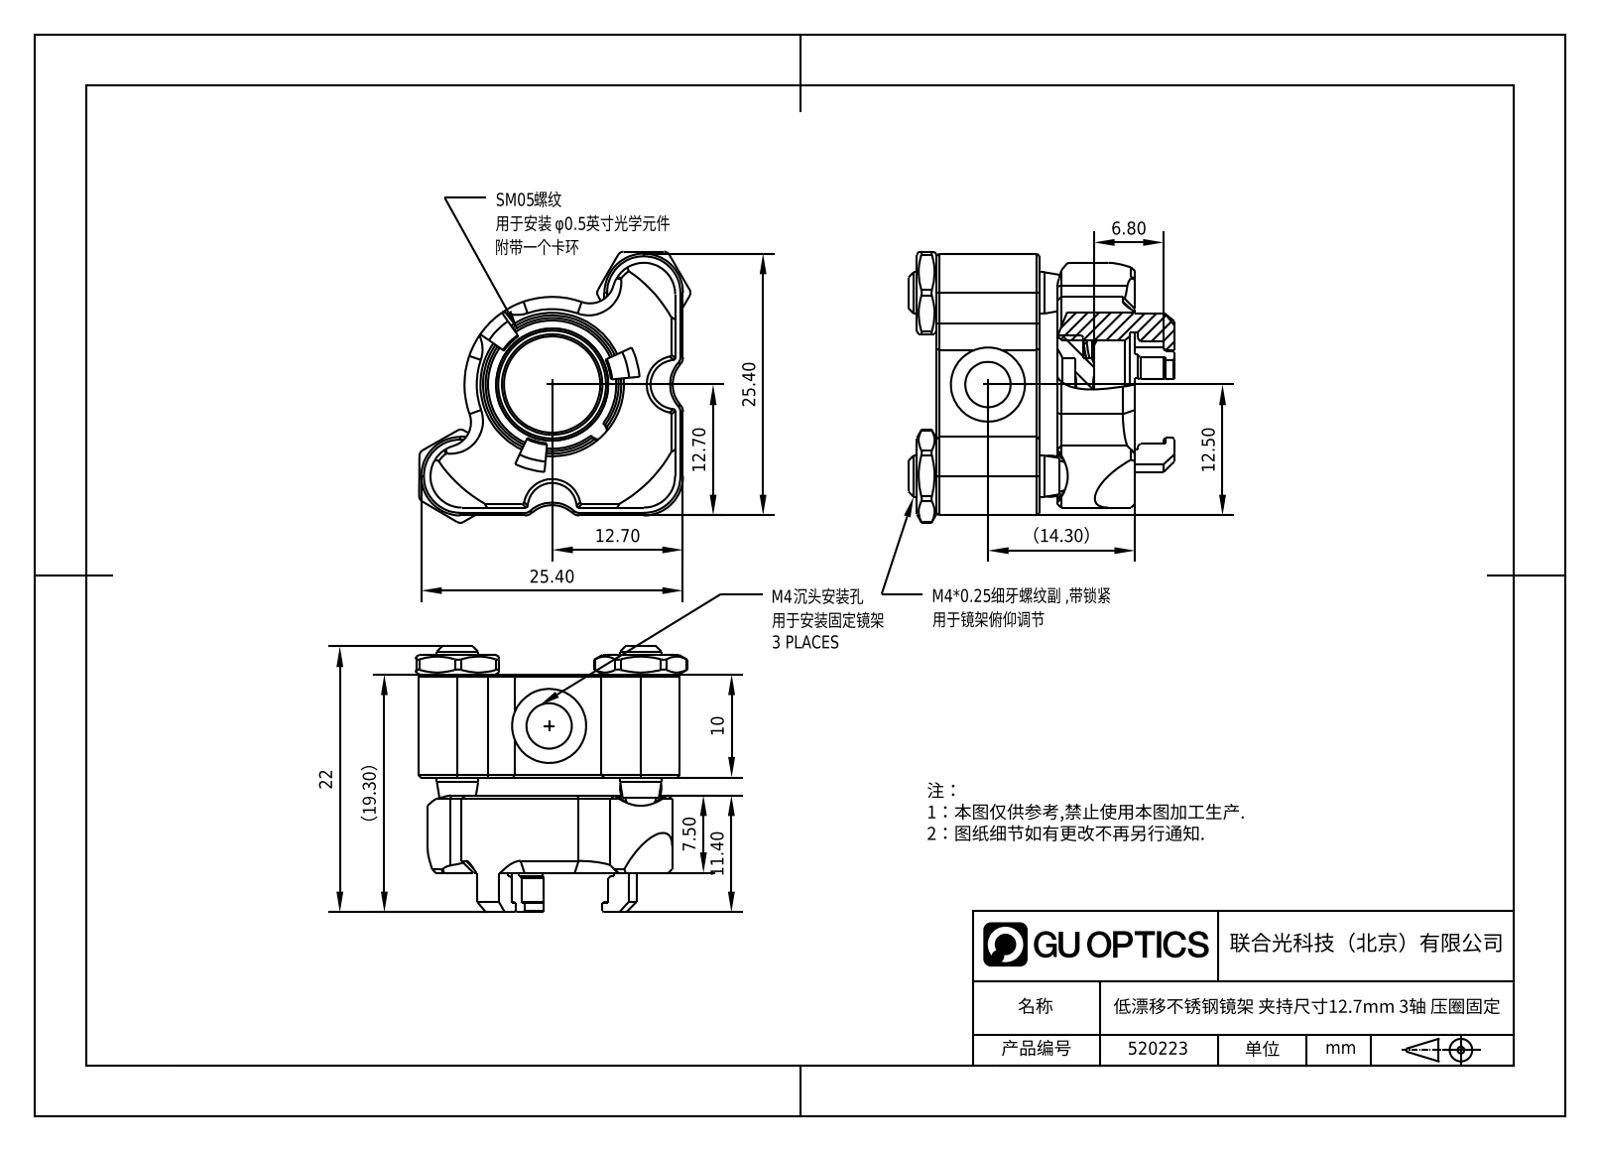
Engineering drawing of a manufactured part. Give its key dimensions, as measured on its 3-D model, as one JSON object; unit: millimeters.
{"part_name": "1.1.20.25_ZJO-PSM0.5-3; ZFK不锈钢透镜卡环压圈_1.8.9.1_ZFKS-K05; DXS-0425标准细牙螺丝_3.2.2.3-DXS-0425-16; 32.5.1-6，蓝宝石垫片，A (+5 more)", "step_written_by": "SolidWorks 2021 (CONFIG_CONTROL_DESIGN)", "units": "millimeters", "bodies": {"solids": 20, "faces": 583, "planar": 193, "cylindrical": 171, "other": 219}, "overall_size": [26.33, 26.31, 26.14], "volume_mm3": 4487, "surface_area_mm2": 5871, "round_holes": [[3.4, 5], [1.6, 4], [2.99, 3], [3.75, 3], [4, 3], [4.35, 3], [2, 2], [4.4, 2], [7.2, 2], [11.19, 1], [12.9, 1], [13.92, 1]], "round_bosses_or_shafts": [[2.5, 6], [2, 2], [13.59, 1]], "partial_cylinders_radius": [[0.6, 18], [1, 8], [3.05, 3], [3.81, 3], [0.19, 2], [0.19, 2], [2.38, 2], [2.39, 2]], "face_to_face_distances": [2, 10, 9.54, 19.54, 12, 7.54, 1.9, 0.76, 0.77, 8], "hole_center_spacings": [9.72, 11.74, 12.83, 4.95, 4.96, 7.87, 12.57, 18.46]}
